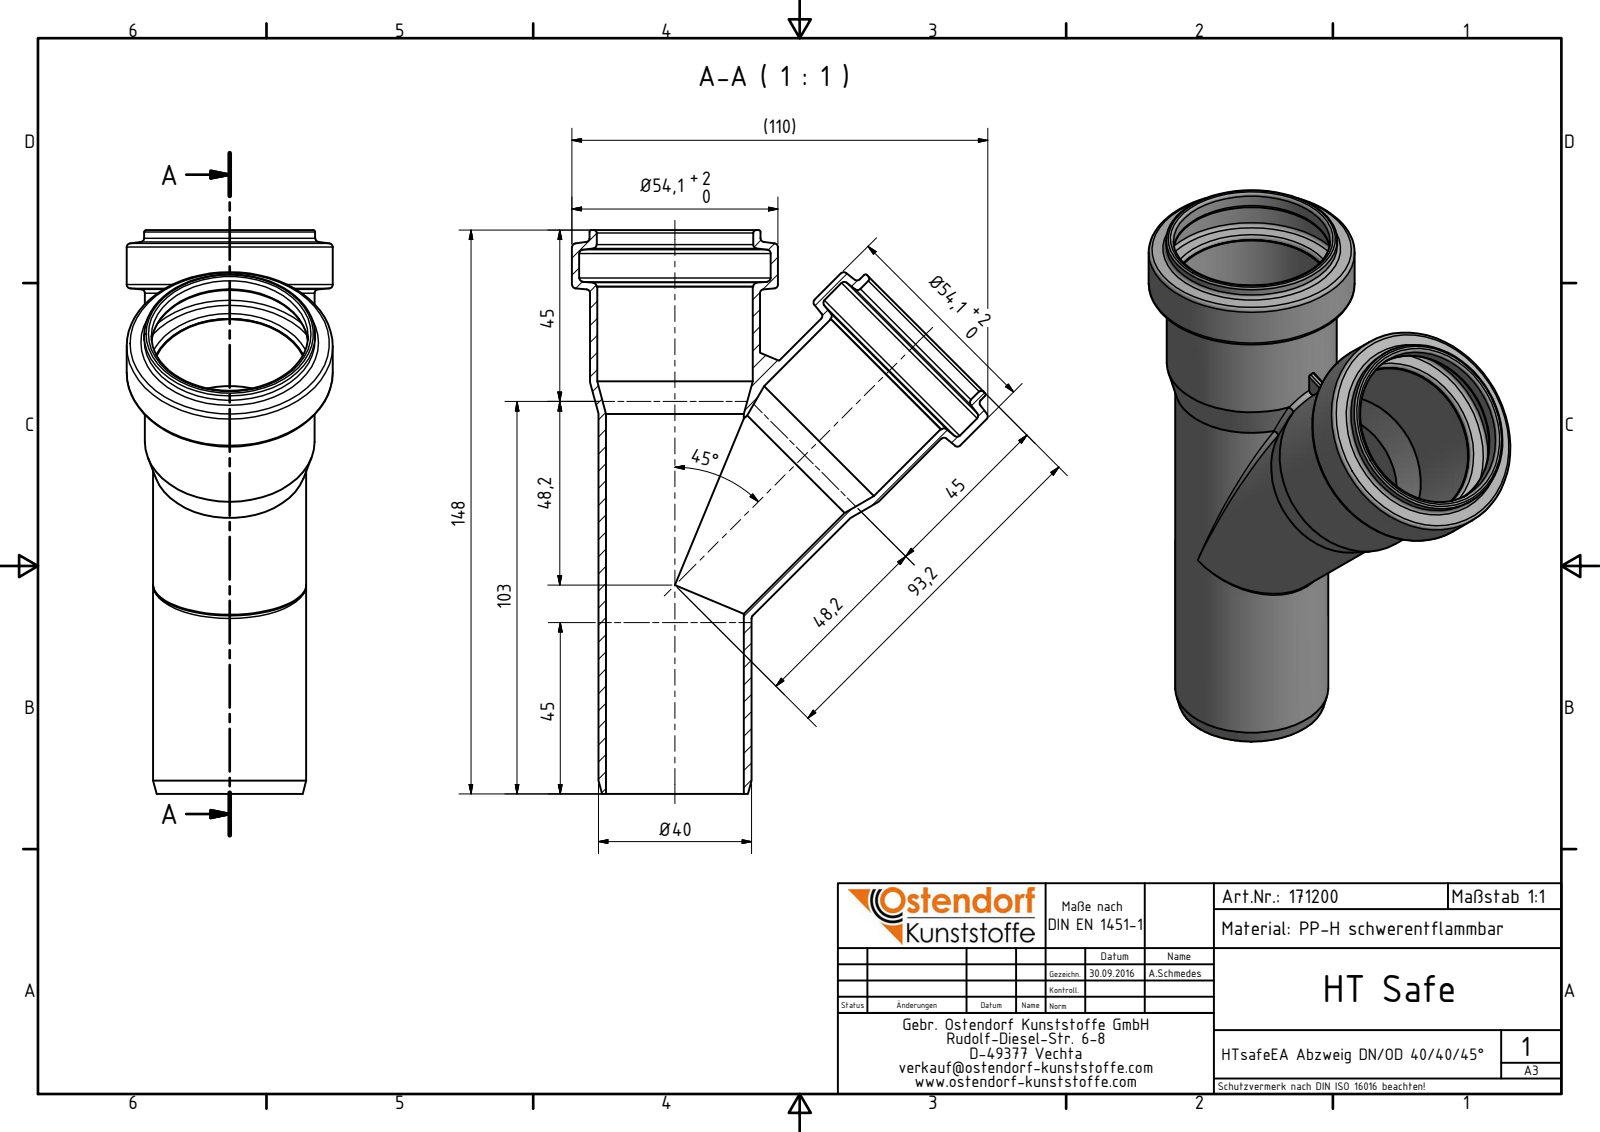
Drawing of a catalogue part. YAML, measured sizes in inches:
part_name: "171200 HTsafeEA DN_OD 40_40_45°"
step_written_by: "Autodesk Inventor 2016 (AUTOMOTIVE_DESIGN)"
units: inches
bodies: {solids: 1, faces: 69, planar: 8, cylindrical: 21, other: 40}
overall_size: [5.827, 4.299, 2.13]
volume: 3.458
surface_area: 89.94
round_holes:
  - {diameter: 1.425, count: 2}
  - {diameter: 1.606, count: 2}
  - {diameter: 1.618, count: 2}
  - {diameter: 1.98, count: 2}
round_bosses_or_shafts:
  - {diameter: 2.13, count: 2}
  - {diameter: 1.768, count: 2}
  - {diameter: 1.756, count: 2}
  - {diameter: 1.583, count: 2}
partial_cylinders:
  - {radius: 0.02, count: 2}
face_to_face_distances: [5.827, 0.587, 5.24, 0.075]
